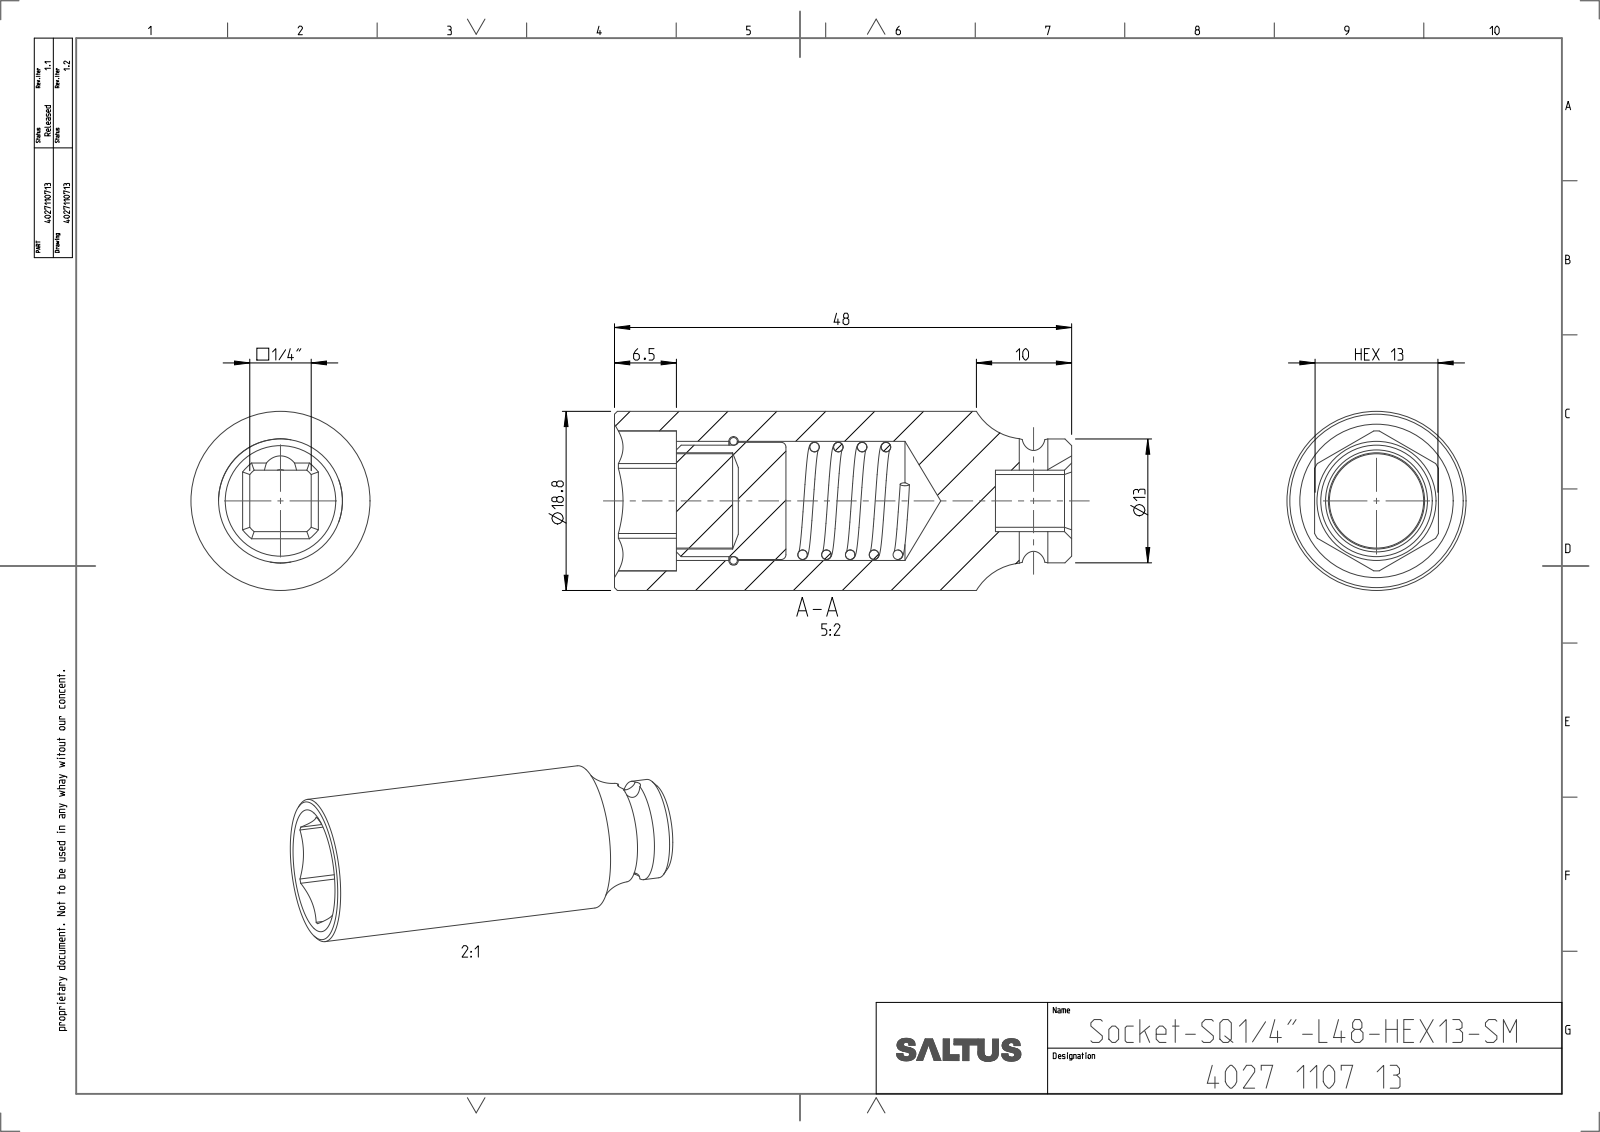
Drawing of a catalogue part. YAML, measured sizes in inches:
part_name: "4027110713"
step_written_by: "CREO PARAMETRIC BY PTC INC, 2022414 (CONFIG_CONTROL_DESIGN)"
units: inches
bodies: {solids: 4, faces: 91, planar: 26, cylindrical: 31, other: 34}
overall_size: [1.89, 0.74, 0.74]
volume: 0.544
surface_area: 9.934
round_holes:
  - {diameter: 0.118, count: 1}
  - {diameter: 0.398, count: 1}
  - {diameter: 0.492, count: 1}
round_bosses_or_shafts:
  - {diameter: 0.74, count: 1}
  - {diameter: 0.512, count: 1}
  - {diameter: 0.484, count: 1}
  - {diameter: 0.461, count: 1}
  - {diameter: 0.39, count: 1}
partial_cylinders:
  - {radius: 0.079, count: 1}
  - {radius: 0.167, count: 1}
  - {radius: 0.289, count: 1}
face_to_face_distances: [0.512, 0.453, 0.256, 0.129, 0.383, 0.22, 0.232, 0.254, 0.709, 0.488]
